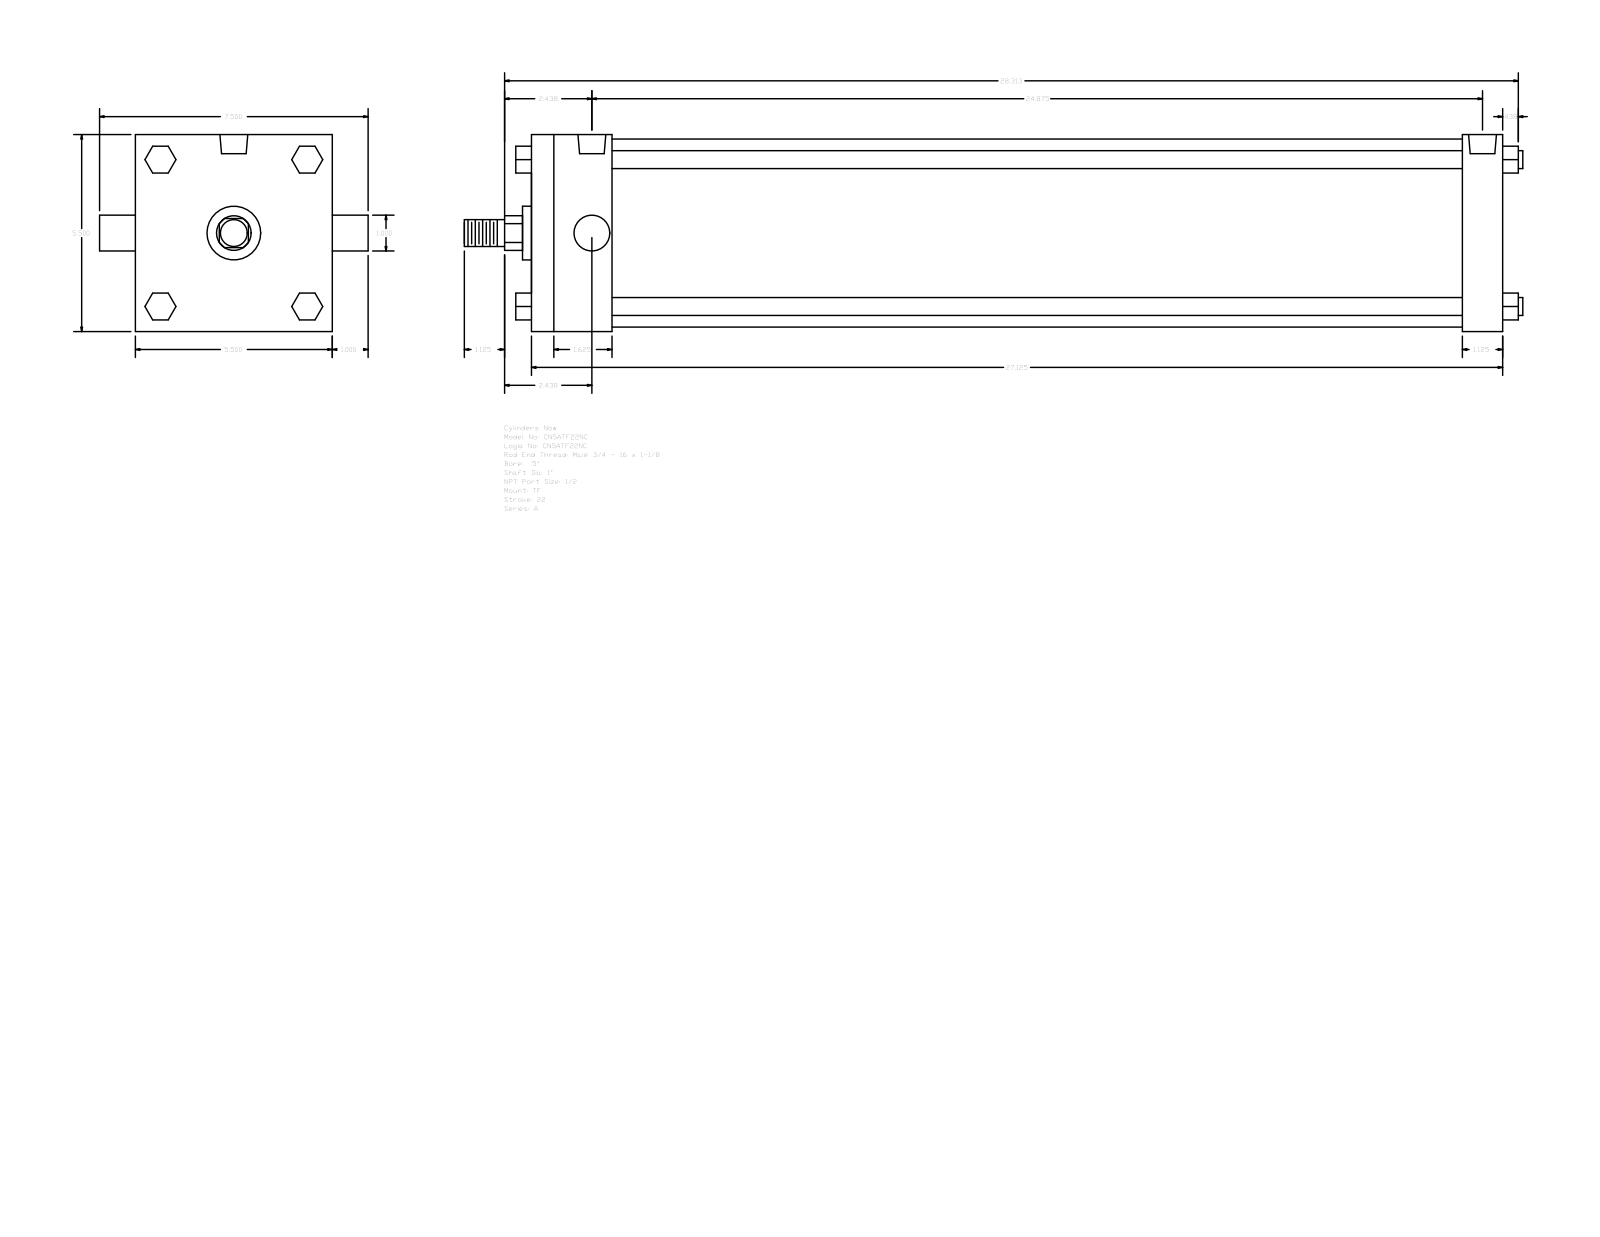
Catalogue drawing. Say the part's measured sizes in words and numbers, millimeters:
The part is named "A_TF__0500_1". Its 3-D file was written by "GSSL Pune (CONFIG_CONTROL_DESIGN)". It is 0 solids with 120 faces: 92 planar, 28 cylindrical and 0 other. Overall it measures 750.89 by 190.5 by 139.7 millimeters. Round holes: 3 of diameter 8.73, 2 of diameter 19.77. Round bosses or shafts: 4 of diameter 12.7, 2 of diameter 25.4, 1 of diameter 133.35, 1 of diameter 38.1, 1 of diameter 19.05. Partial cylindrical surfaces (rounded edges, fillets, slot ends): 1 of radius 12.29. The main face-to-face distances are 139.7, 688.97, 28.57, 660.4, 57.15, 603.25, 631.82, 19.05, 52.07, 90.18. The hole center spacings are 2.39, 629.44, 627.05, 631.83.
